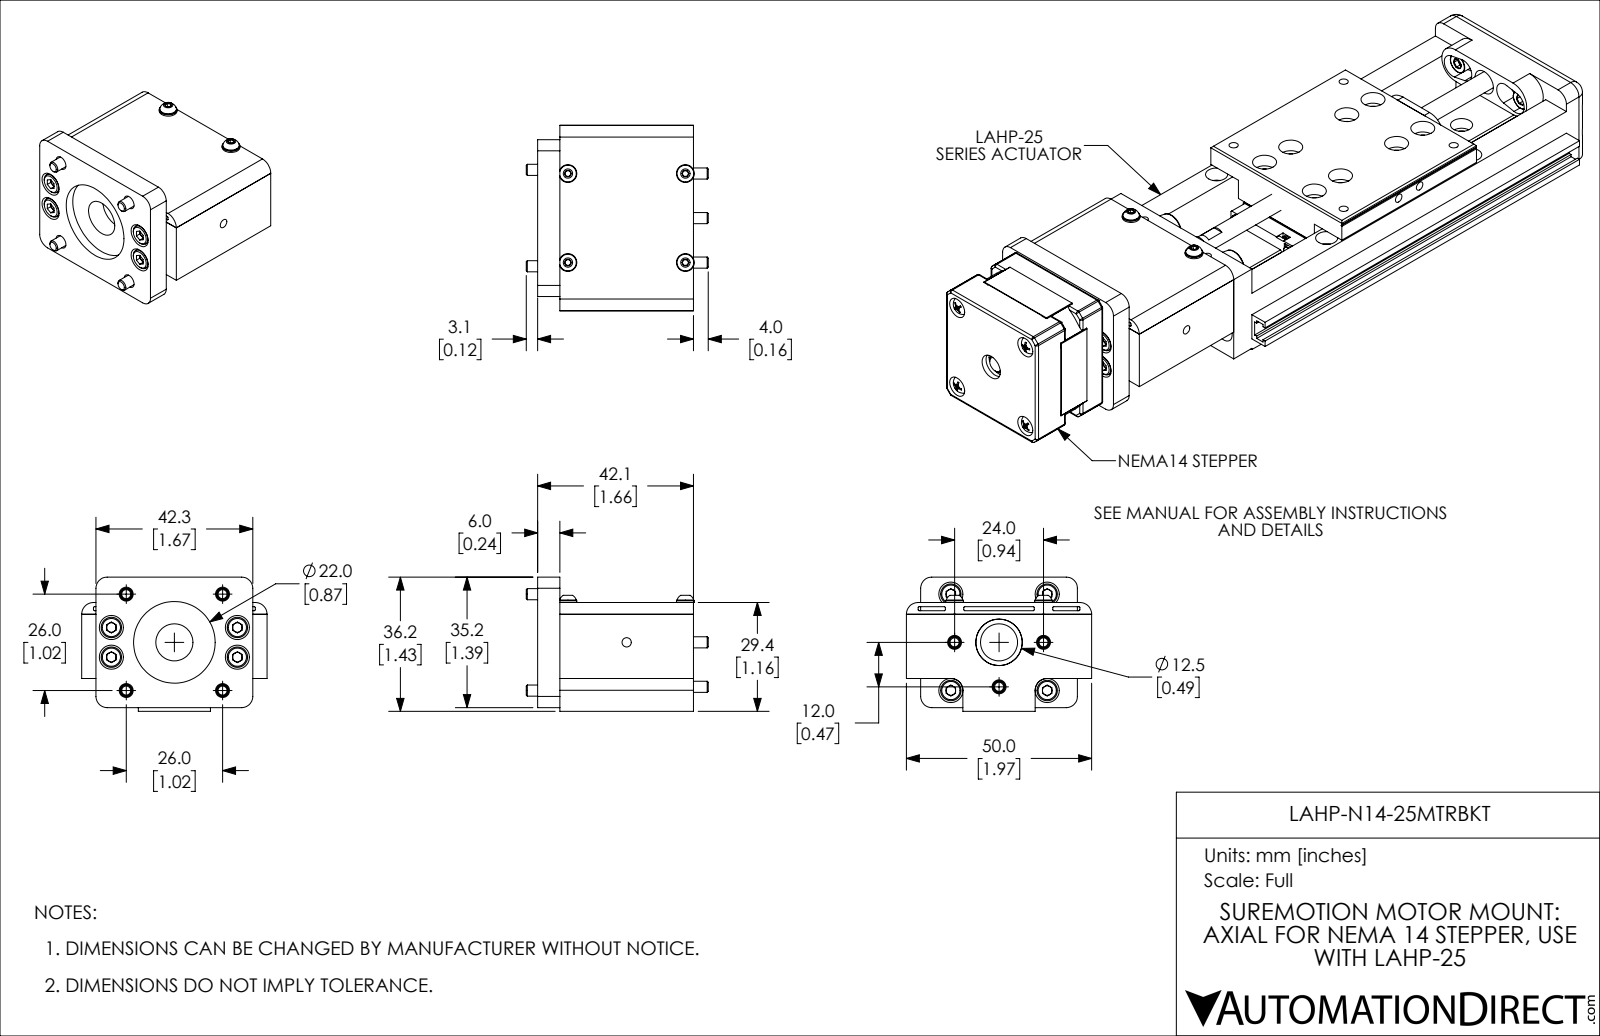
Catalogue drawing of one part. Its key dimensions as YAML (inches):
part_name: "LAHP-N14-25MTRBKT"
step_written_by: "SolidWorks 2019 (CONFIG_CONTROL_DESIGN)"
units: inches
bodies: {solids: 40, faces: 1181, planar: 397, cylindrical: 552, other: 232}
overall_size: [1.969, 1.933, 1.425]
volume: 2.057
surface_area: 38.54
round_holes:
  - {diameter: 0.126, count: 11}
  - {diameter: 0.148, count: 11}
  - {diameter: 0.256, count: 11}
  - {diameter: 0.098, count: 5}
  - {diameter: 0.081, count: 4}
  - {diameter: 0.106, count: 4}
  - {diameter: 0.122, count: 4}
  - {diameter: 0.394, count: 1}
  - {diameter: 0.493, count: 1}
  - {diameter: 0.867, count: 1}
round_bosses_or_shafts:
  - {diameter: 0.217, count: 11}
  - {diameter: 0.118, count: 11}
  - {diameter: 0.219, count: 4}
  - {diameter: 0.189, count: 4}
  - {diameter: 0.177, count: 4}
  - {diameter: 0.112, count: 4}
  - {diameter: 0.098, count: 4}
  - {diameter: 0.08, count: 4}
partial_cylinders:
  - {radius: 0.01, count: 12}
  - {radius: 0.125, count: 12}
  - {radius: 0.118, count: 4}
face_to_face_distances: [0.125, 1.42, 0.236, 0.08, 0.045, 1.656, 0.682, 0.762, 0.807, 0.065]
hole_center_spacings: [0.687, 0.513, 1.109, 0.252, 0.388, 0.724, 1.024, 1.152]
